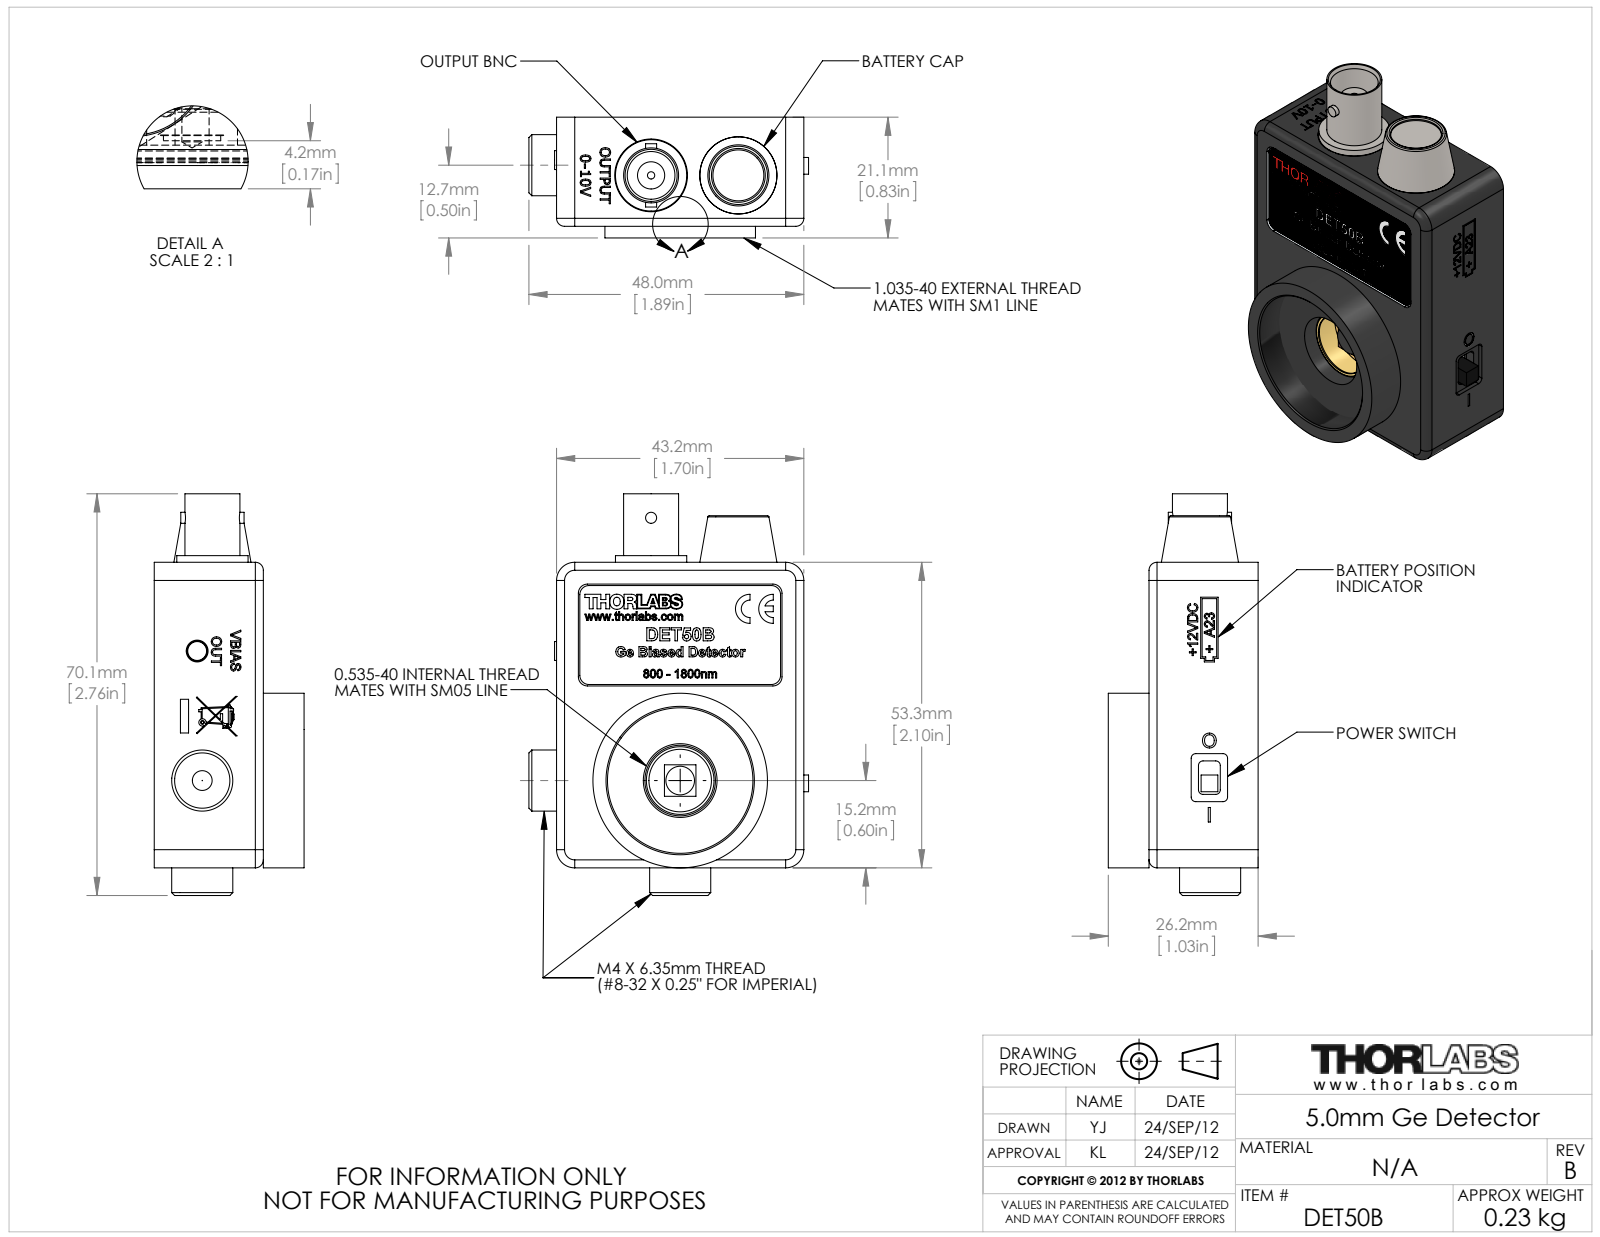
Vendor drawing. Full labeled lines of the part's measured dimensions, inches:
Part name (STEP PRODUCT): 13124-999; SH2S019-1; 13124-D02_PDA25K-LB1; 24704-E0W (+8 more)
STEP written by: SolidWorks 2011 (AUTOMOTIVE_DESIGN)
Units: inches
Bodies: 24 solids, 2423 faces (1213 planar, 480 cylindrical, 730 other)
Overall size (bounding box): 2.761 × 1.922 × 1.03
Volume: 1.509 in³ · Surface area: 44.55 in²
Round holes (diameter × count): ⌀0.07 ×7, ⌀0.032 ×6, ⌀0.05 ×5, ⌀0.096 ×4, ⌀0.098 ×4, ⌀0.125 ×4, ⌀0.2 ×4, ⌀0.03 ×3, ⌀0.15 ×3, ⌀0.025 ×2, ⌀0.037 ×2, ⌀0.045 ×2
Round bosses / shafts (diameter × count): ⌀0.086 ×7, ⌀0.147 ×4, ⌀0.039 ×4, ⌀0.14 ×3, ⌀0.063 ×3, ⌀0.42 ×2, ⌀0.236 ×2, ⌀0.21 ×2
Partial cylindrical surfaces — rounded edges, fillets, slot ends (radius × count): R0.125 ×26, R0.031 ×8, R0.095 ×8, R0.004 ×6, R0.02 ×6, R0.016 ×4, R0.055 ×4, R0.063 ×4
Main face-to-face distances: 0.063, 0.452, 0.1, 0.515, 0.07, 0.05, 0.228, 0.165, 0.68, 0.617
Hole centre spacings: 0.203, 0.079, 0.098, 0.126, 0.128, 0.28, 0.412, 0.426
